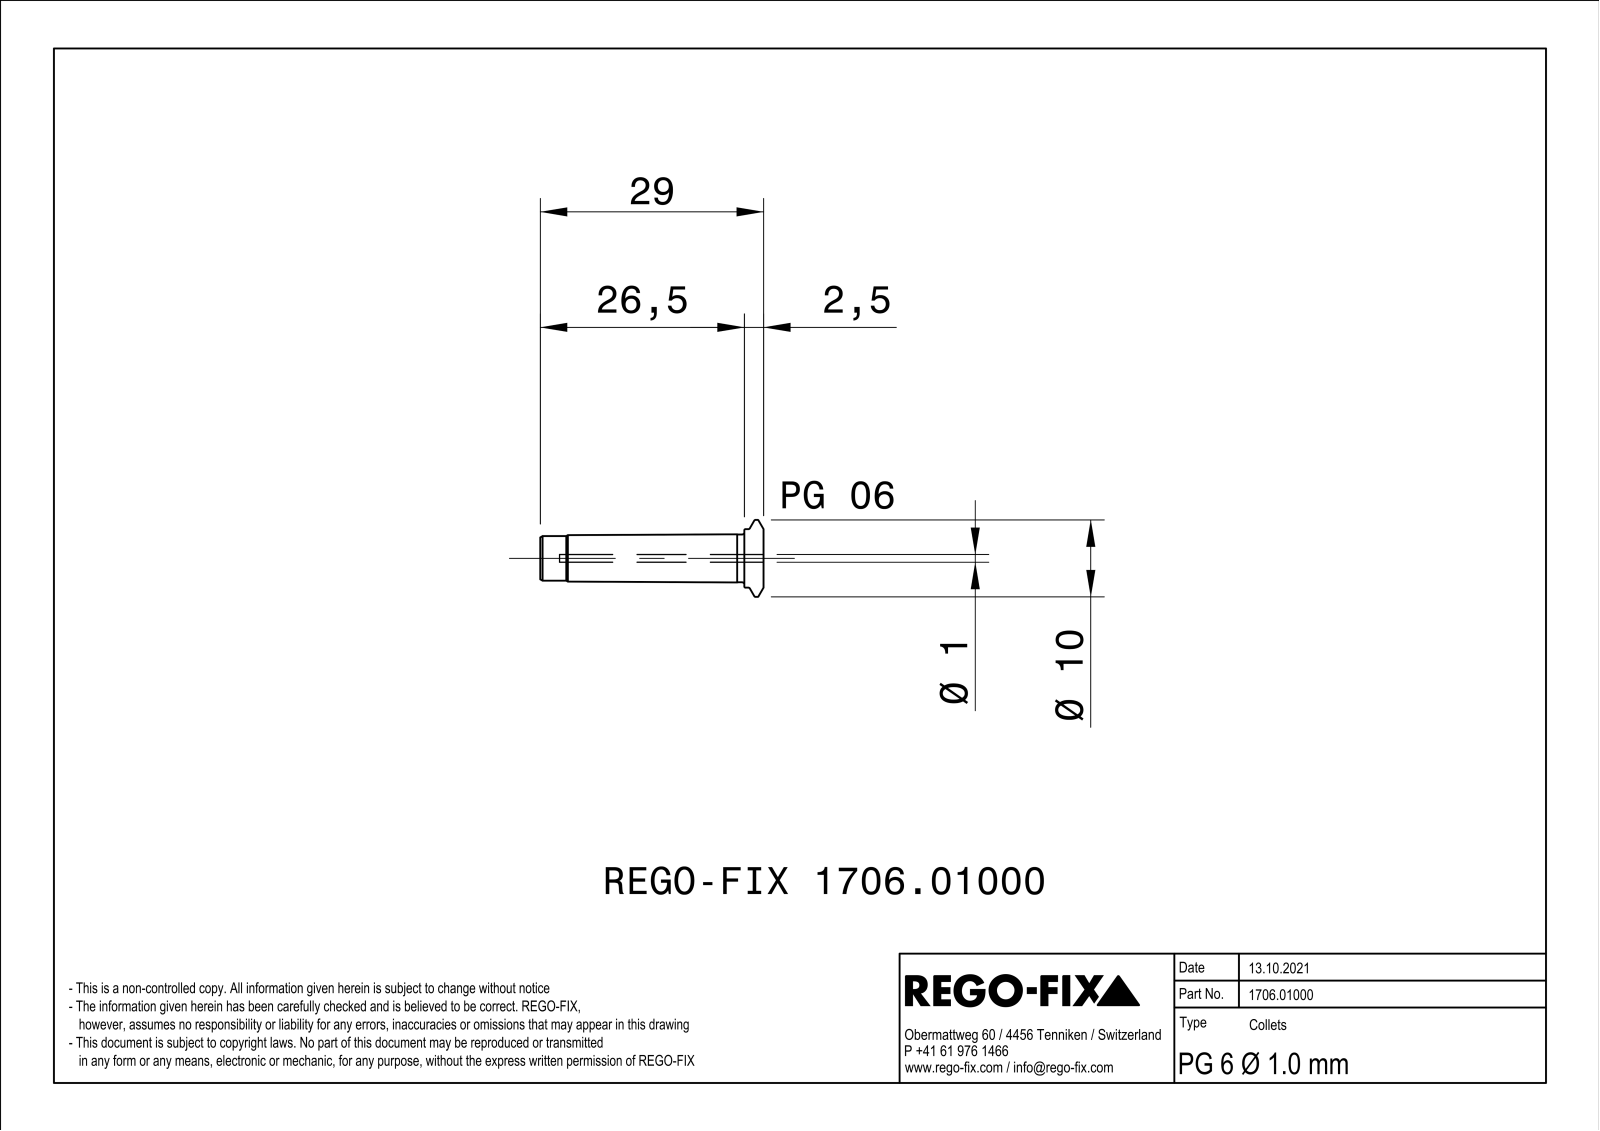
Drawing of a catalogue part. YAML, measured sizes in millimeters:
part_name: "0024264"
step_written_by: "SIEMENS PLM Software Solid Edge ST10 (AUTOMOTIVE_DESIGN)"
units: millimeters
bodies: {solids: 1, faces: 62, planar: 17, cylindrical: 13, other: 32}
overall_size: [29, 10, 9.99]
volume: 791
surface_area: 1055
round_holes:
  - {diameter: 1, count: 1}
  - {diameter: 3.46, count: 1}
round_bosses_or_shafts:
  - {diameter: 10, count: 1}
  - {diameter: 7.6, count: 1}
  - {diameter: 6.2, count: 1}
  - {diameter: 5.8, count: 1}
face_to_face_distances: [0.45, 0.46, 29, 2.5, 26.5]
